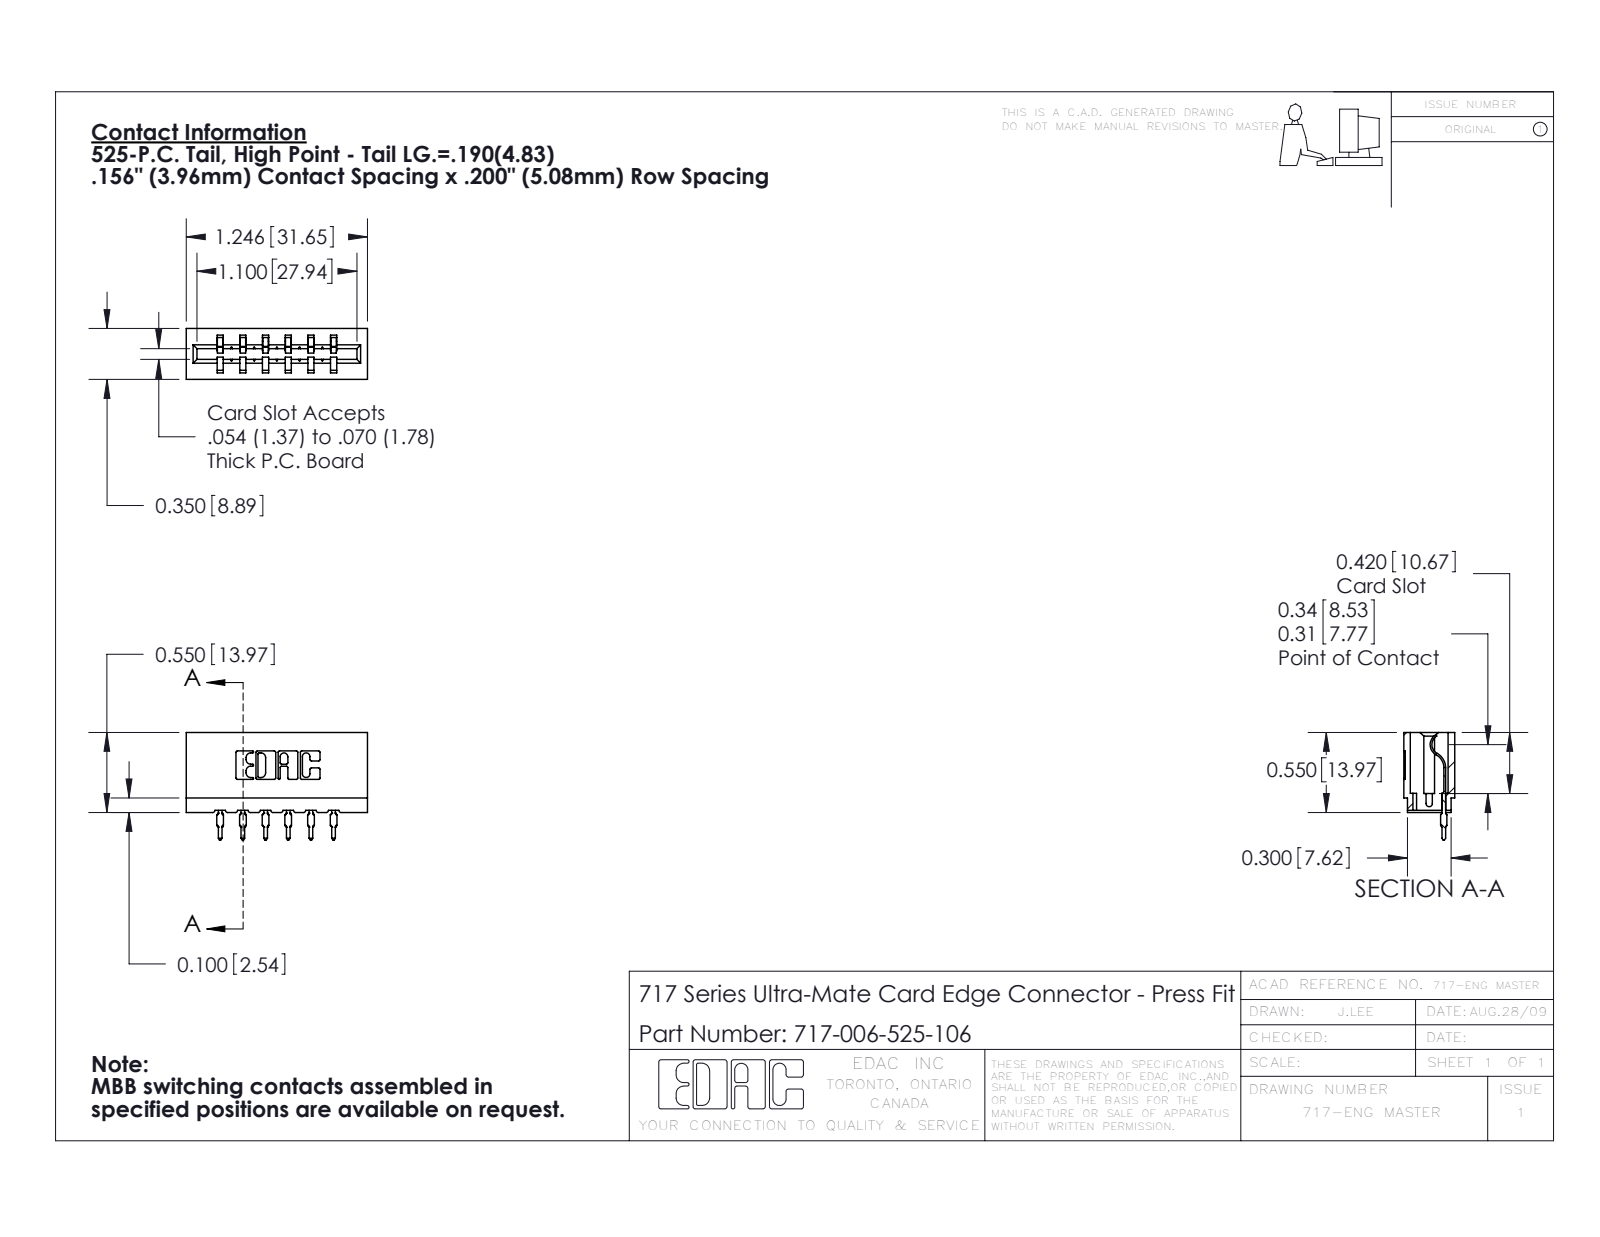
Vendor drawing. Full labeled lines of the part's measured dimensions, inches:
Part name (STEP PRODUCT): 717 Part_Insulator Option - 06; 745-292-001_525; 717-006-525-106
STEP written by: SolidWorks 2016 (CONFIG_CONTROL_DESIGN)
Units: inches
Bodies: 7 solids, 772 faces (462 planar, 154 cylindrical, 156 other)
Overall size (bounding box): 1.246 × 0.739 × 0.35
Volume: 0.173 in³ · Surface area: 5.528 in²
Partial cylindrical surfaces — rounded edges, fillets, slot ends (radius × count): R0.01 ×22, R0.015 ×12, R0.021 ×12, R0.007 ×6, R0.031 ×6, R0.005 ×4, R0.011 ×4, R0.026 ×3
Main face-to-face distances: 0.212, 0.156, 0.138, 0.35, 0.198, 0.312, 0.468, 0.312, 0.624, 0.042
